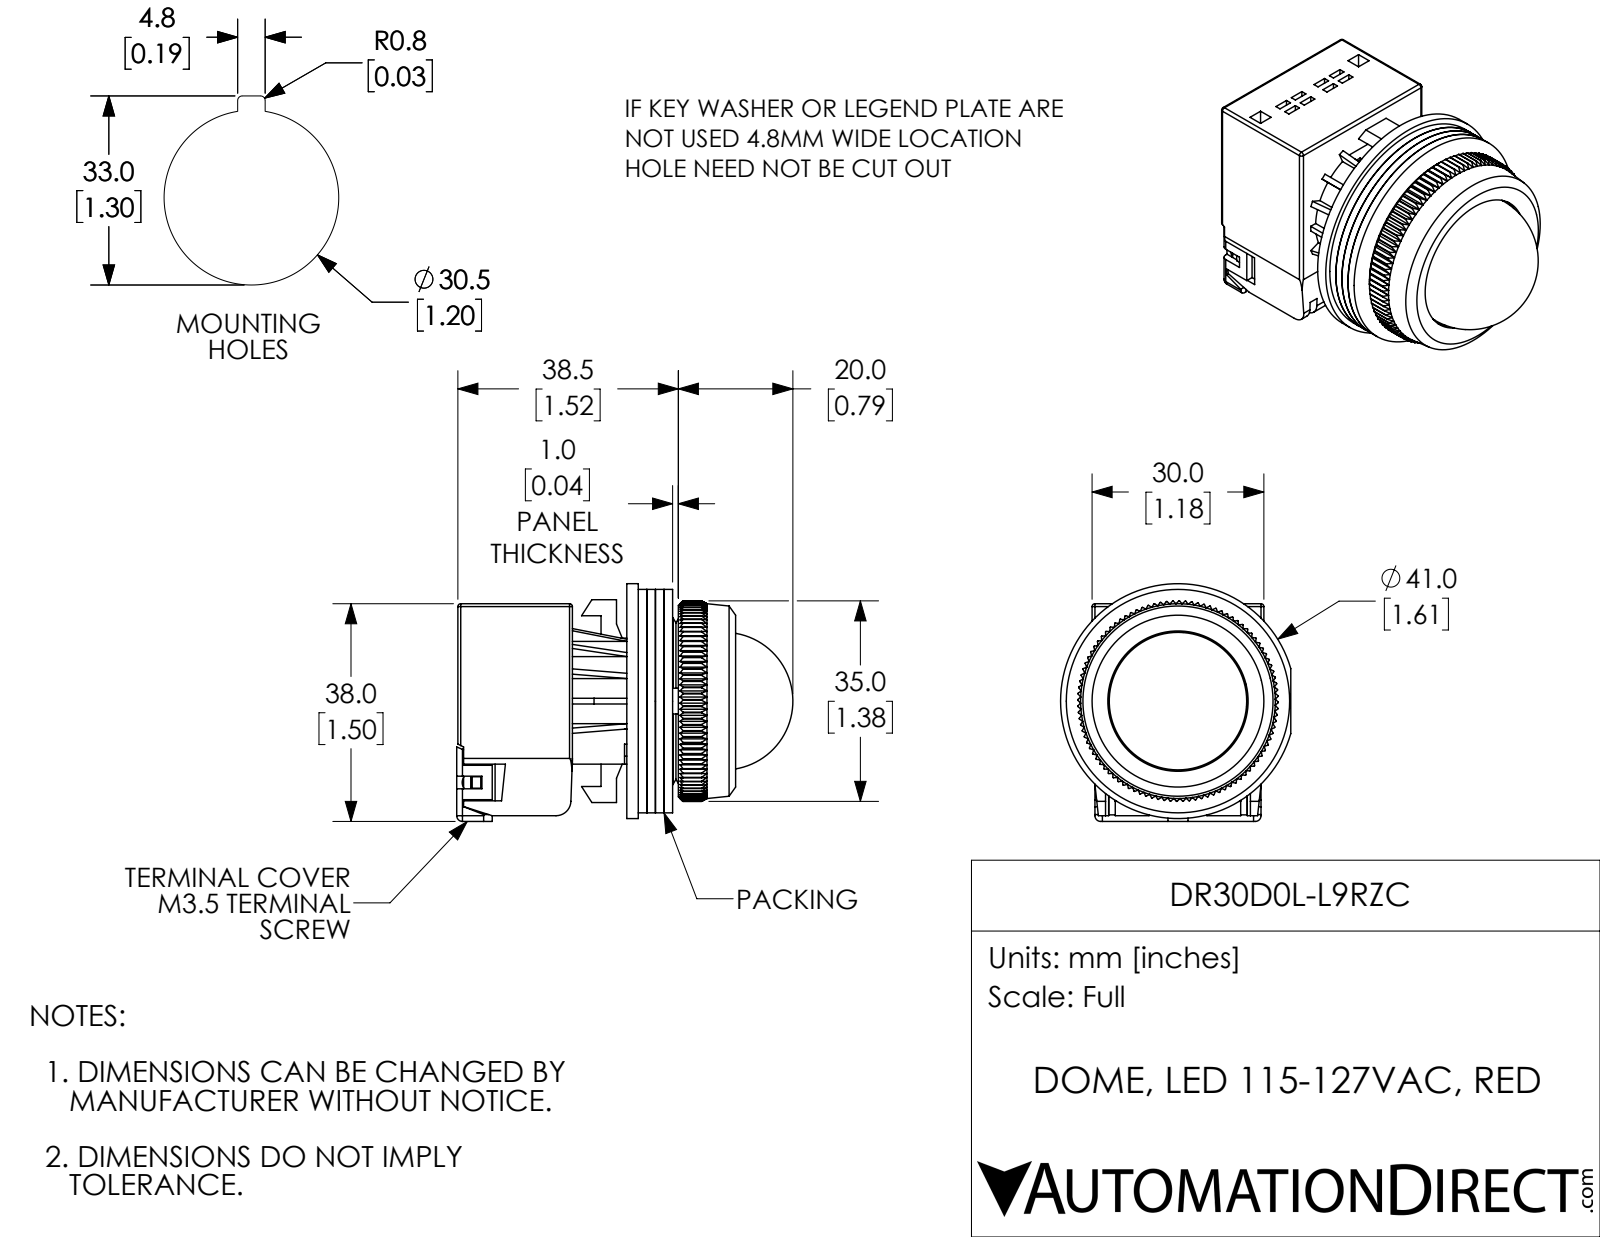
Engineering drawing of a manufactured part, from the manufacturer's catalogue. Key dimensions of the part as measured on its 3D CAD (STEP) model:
Part name (STEP PRODUCT): DR30D0L-L9RZC
STEP written by: SolidWorks 2017 (AUTOMOTIVE_DESIGN)
Units: inches
Bodies: 18 solids, 1544 faces (945 planar, 353 cylindrical, 246 other)
Overall size (bounding box): 2.309 × 1.634 × 1.583
Volume: 2.184 in³ · Surface area: 48.71 in²
Round holes (diameter × count): ⌀0.118 ×2, ⌀0.122 ×2, ⌀0.138 ×2, ⌀0.276 ×2, ⌀0.362 ×1, ⌀0.433 ×1, ⌀0.461 ×1, ⌀0.543 ×1, ⌀0.563 ×1, ⌀0.583 ×1, ⌀0.63 ×1, ⌀0.72 ×1
Round bosses / shafts (diameter × count): ⌀0.232 ×2, ⌀1.614 ×1, ⌀1.535 ×1, ⌀1.16 ×1, ⌀0.945 ×1, ⌀0.858 ×1, ⌀0.819 ×1, ⌀0.799 ×1
Partial cylindrical surfaces — rounded edges, fillets, slot ends (radius × count): R0.039 ×14, R0.008 ×8, R0.02 ×8, R0.065 ×3, R0.029 ×1, R0.068 ×1, R0.079 ×1, R0.102 ×1
Main face-to-face distances: 0.059, 0.118, 0.177, 0.039, 0.315, 0.197, 0.512, 0.689, 0.374, 1.161
Hole centre spacings: 0.704, 0.63
